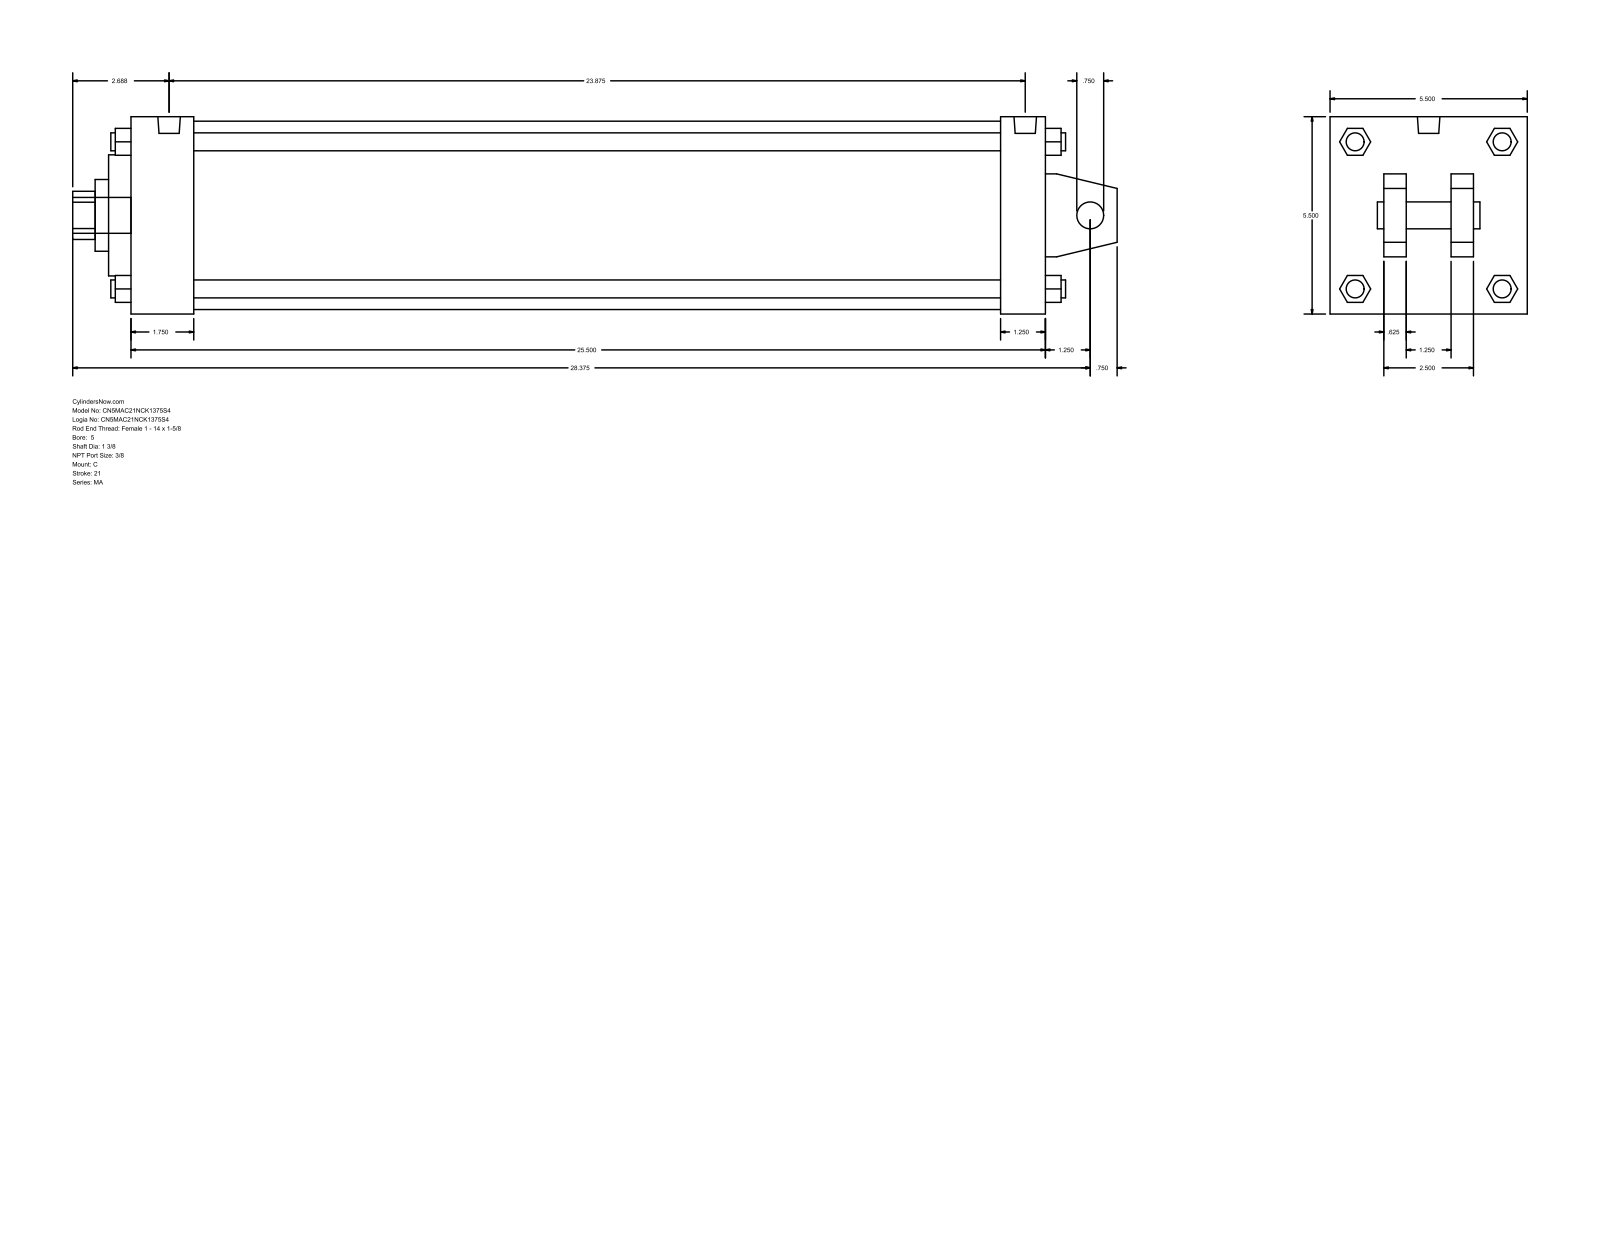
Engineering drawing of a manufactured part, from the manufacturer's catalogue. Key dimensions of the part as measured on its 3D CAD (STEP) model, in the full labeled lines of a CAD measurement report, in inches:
Part name (STEP PRODUCT): MA_C__0500_1.375
STEP written by: GSSL Pune (CONFIG_CONTROL_DESIGN)
Units: inches
Bodies: 0 solids, 141 faces (109 planar, 32 cylindrical, 0 other)
Overall size (bounding box): 29.125 × 5.5 × 5.5
Round holes (diameter × count): ⌀0.75 ×1, ⌀1.375 ×1, ⌀2 ×1, ⌀3.375 ×1, ⌀5.25 ×1
Round bosses / shafts (diameter × count): ⌀0.5 ×4, ⌀0.437 ×4, ⌀0.627 ×2, ⌀1 ×1
Partial cylindrical surfaces — rounded edges, fillets, slot ends (radius × count): R0.672 ×1
Main face-to-face distances: 5.5, 25.5, 0.625, 24.25, 1.25, 1.75, 22.5, 23.75, 1.5, 4
